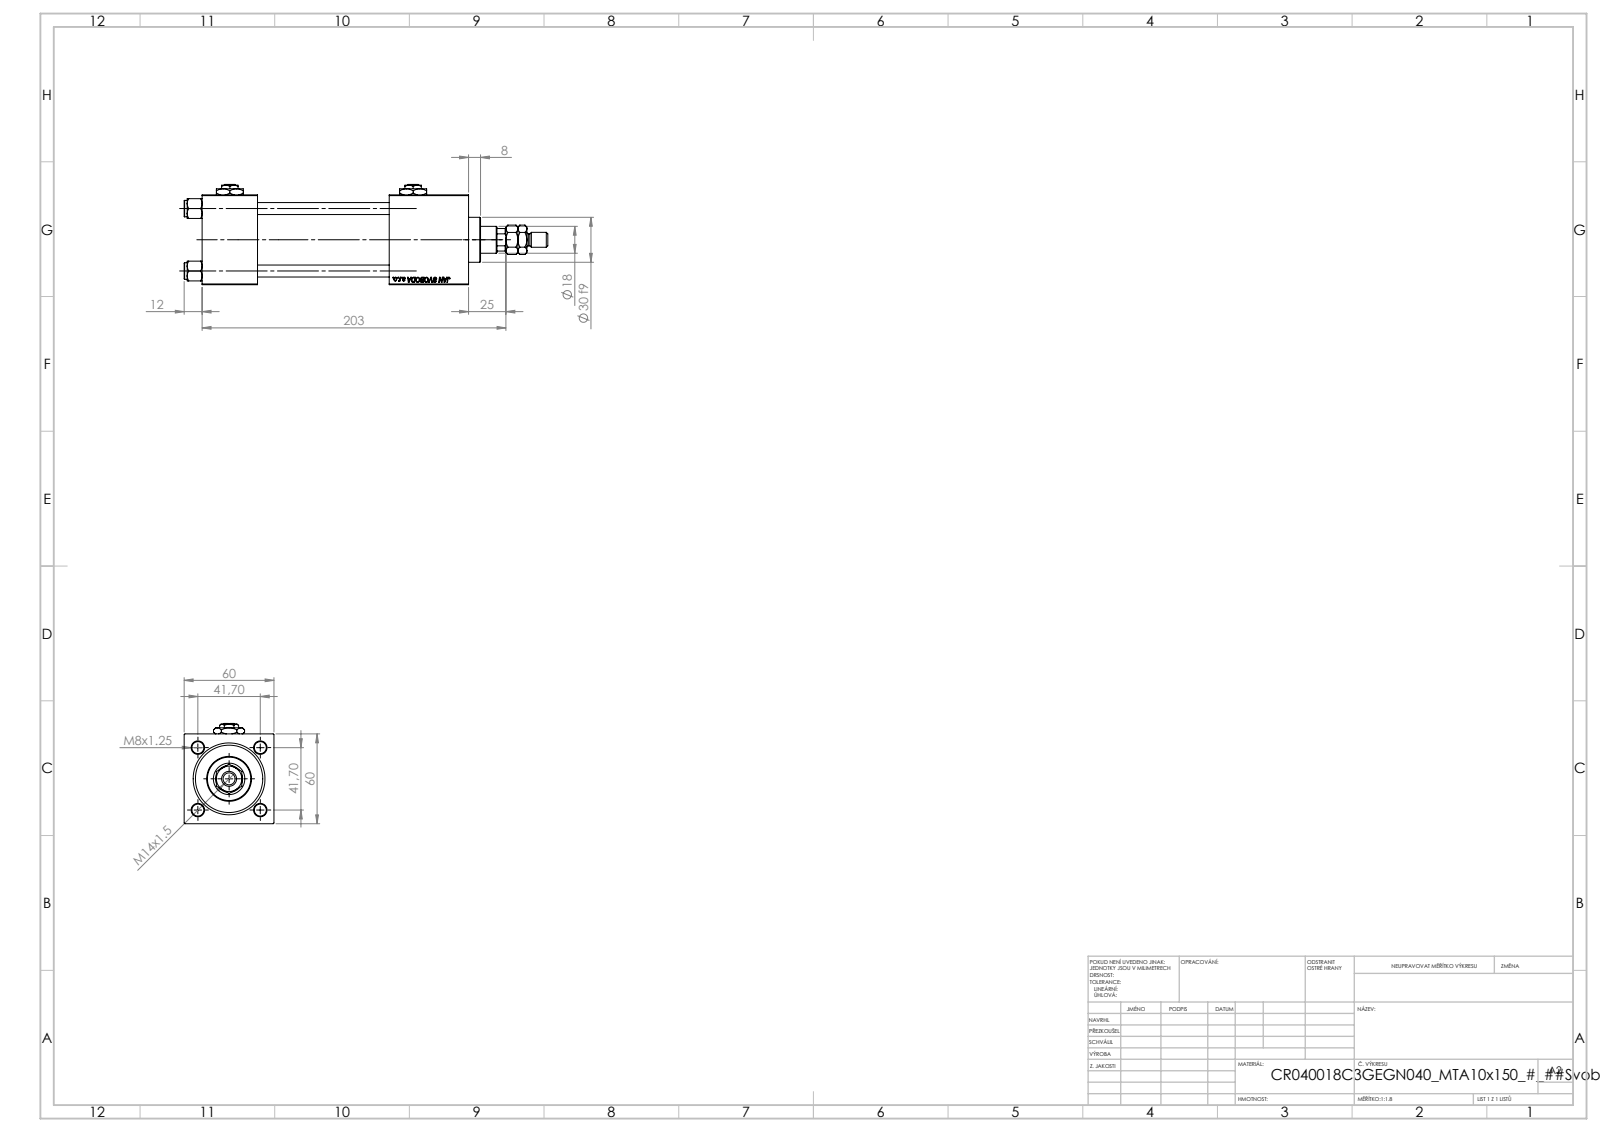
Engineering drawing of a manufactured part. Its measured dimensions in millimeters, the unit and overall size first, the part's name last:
Units: millimetres
Overall size (bounding box): 243 × 67 × 60
Round holes (diameter × count): ⌀8 ×4, ⌀7 ×2, ⌀16.66 ×2, ⌀24 ×2, ⌀8.5 ×1, ⌀18 ×1, ⌀21 ×1, ⌀31 ×1, ⌀40 ×1, ⌀45 ×1
Round bosses / shafts (diameter × count): ⌀11 ×4, ⌀46 ×1, ⌀30 ×1, ⌀10 ×1, ⌀8 ×1
Partial cylindrical surfaces — rounded edges, fillets, slot ends (radius × count): R8.5 ×1
Main face-to-face distances: 60, 37, 178, 141, 53, 125, 88, 149.3, 112.3, 24.3
Hole centre spacings: 29.49, 41.7, 58.97, 122.5
Volume: 429 151 mm³ · Surface area: 122 891 mm²
Bodies: 14 solids, 1299 faces (589 planar, 102 cylindrical, 608 other)
Part name (STEP PRODUCT): V215CR_C_TYCINKA; V215CR_VCP_C; MTA; NUT_M5_C (+3 more)
STEP written by: SolidWorks 2019 (CONFIG_CONTROL_DESIGN)
